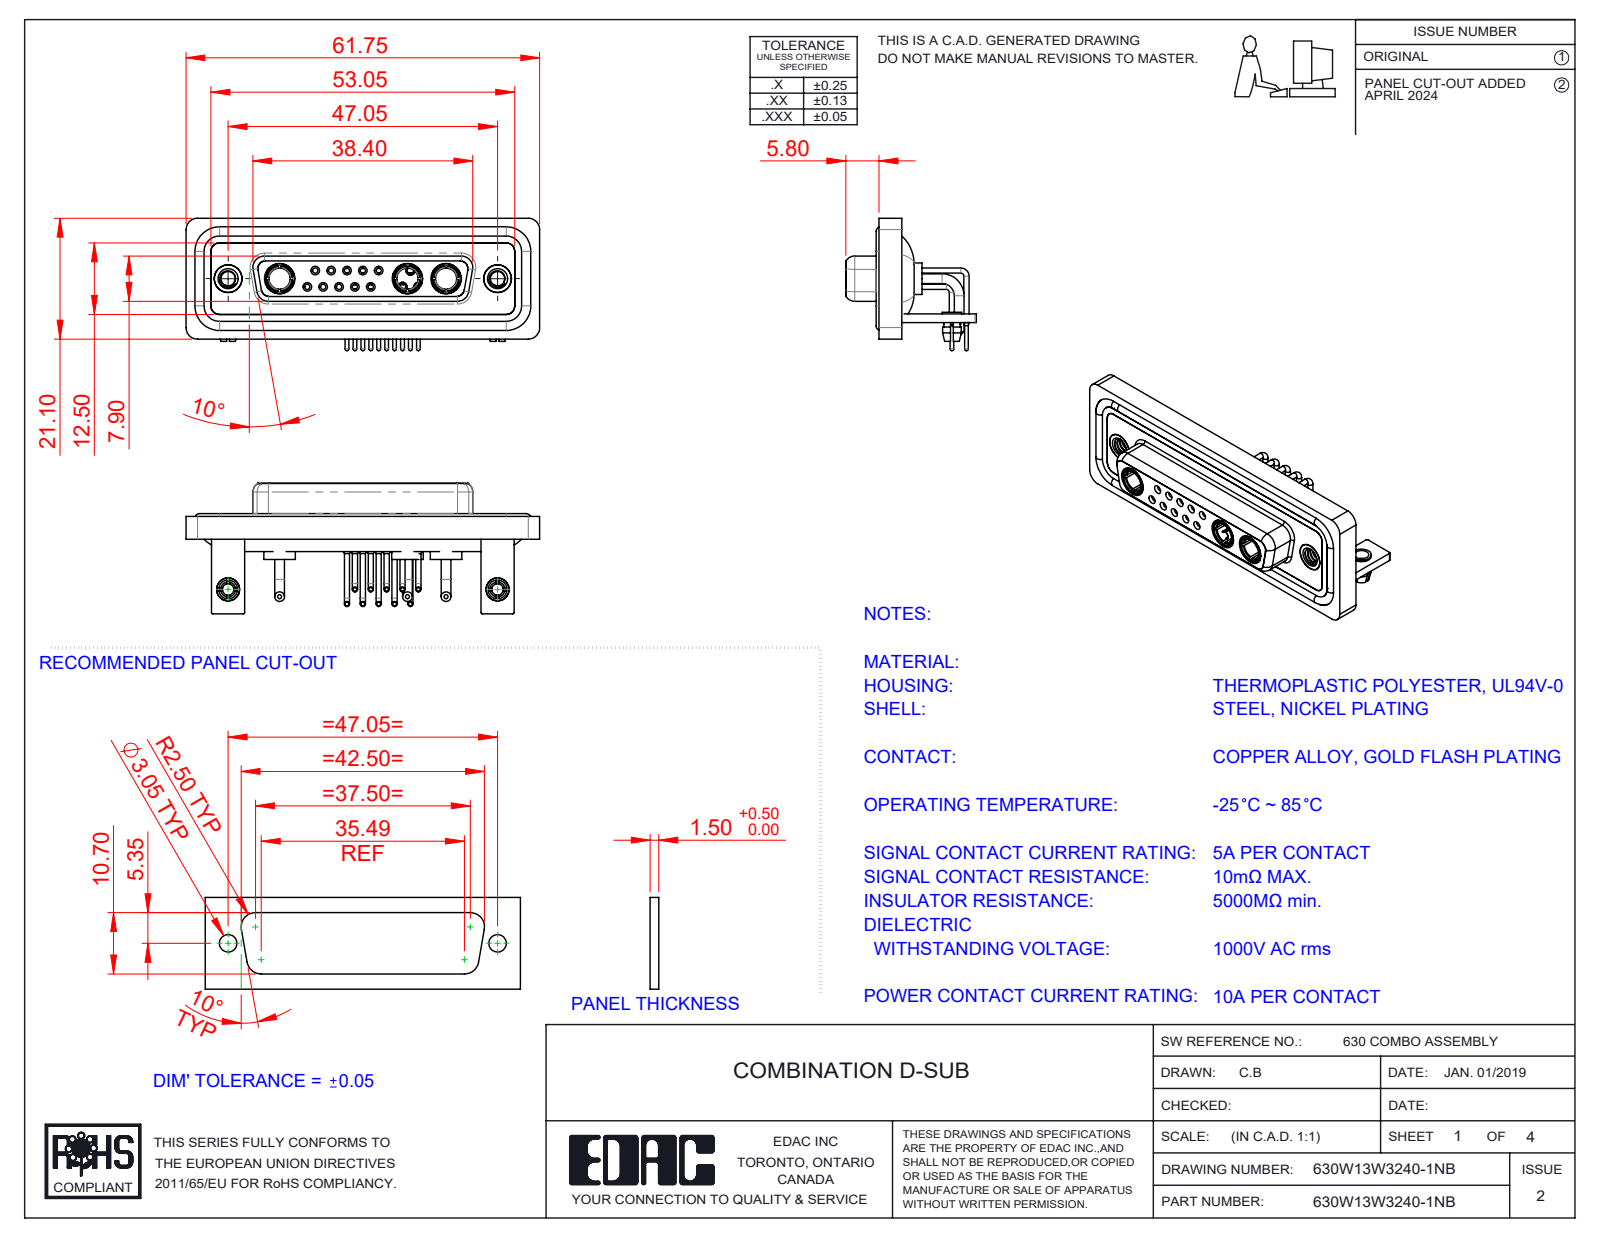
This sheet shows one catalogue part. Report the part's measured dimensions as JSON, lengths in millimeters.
{"part_name": "630Combo Threaded Rivet_A; Power Socket_10A RA; 630Combo Shell Front_25 Contacts; 630W13W3240-1NB (+7 more)", "step_written_by": "SolidWorks 2023 (CONFIG_CONTROL_DESIGN)", "units": "millimeters", "bodies": {"solids": 27, "faces": 1284, "planar": 410, "cylindrical": 547, "other": 327}, "overall_size": [61.75, 23.12, 22.8], "volume_mm3": 8693, "surface_area_mm2": 15093, "round_holes": [[2, 12], [0.9, 10], [1.1, 10], [1.5, 10], [1.6, 5], [1.7, 5], [4.85, 5], [2.5, 4], [3.7, 3], [5.3, 3], [3.2, 2], [4, 2]], "round_bosses_or_shafts": [[0.9, 15], [1.6, 12], [0.65, 10], [1.7, 6], [2, 5], [1.5, 5], [5.5, 3], [5.2, 3]], "partial_cylinders_radius": [[2, 19], [1.5, 18], [0.25, 16], [1.35, 8], [1.6, 8], [0.5, 5], [0.6, 4], [0.65, 4]], "face_to_face_distances": [0.4, 1.8, 2.9, 1.5, 3.7, 4.1, 1.1, 1.4, 1.6, 3.1], "hole_center_spacings": [3.16, 2.77, 5.54, 5.04, 8.31, 5.03, 7.49, 11.08]}
